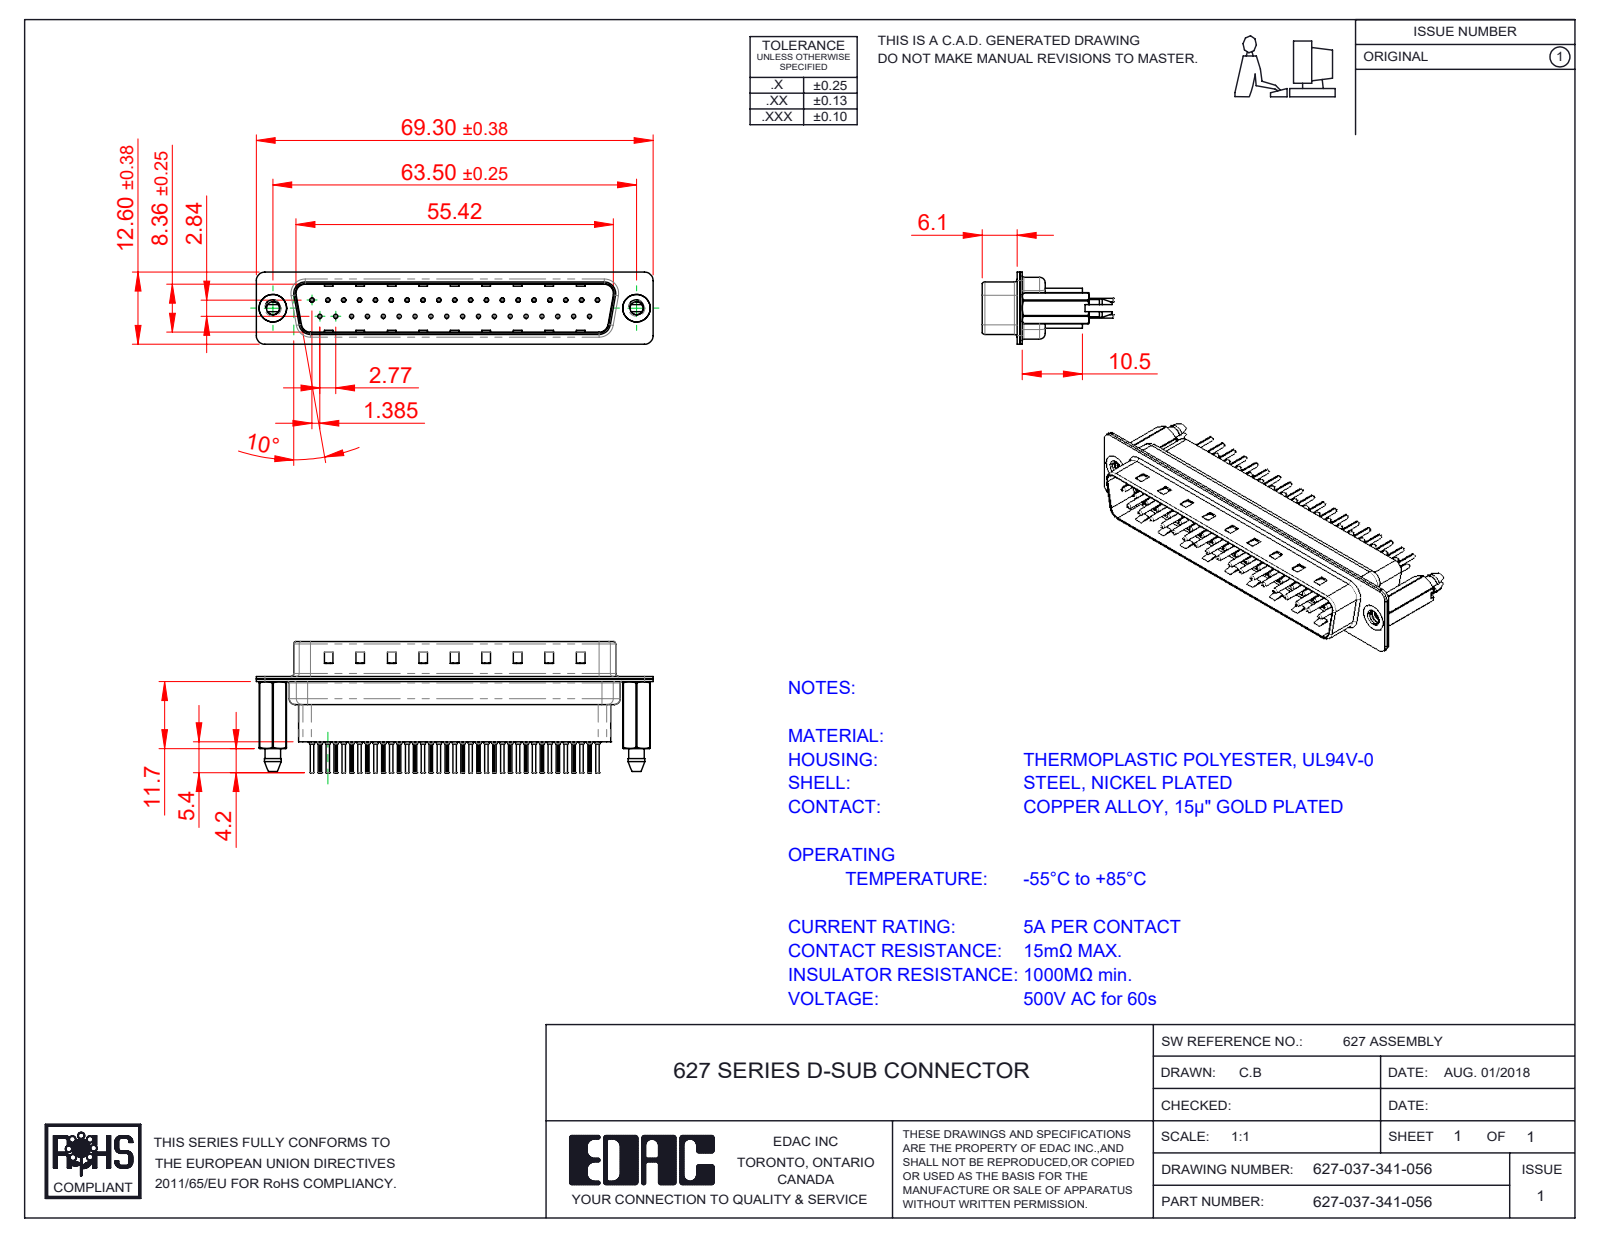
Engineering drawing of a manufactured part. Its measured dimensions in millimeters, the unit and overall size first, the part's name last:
Units: millimetres
Overall size (bounding box): 69.3 × 22.8 × 12.6
Round holes (diameter × count): ⌀0.2 ×37, ⌀0.35 ×37, ⌀1.1 ×37, ⌀1.6 ×37, ⌀2.26 ×2, ⌀4 ×2, ⌀4.8 ×2
Round bosses / shafts (diameter × count): ⌀2 ×37, ⌀1.5 ×37, ⌀0.75 ×37, ⌀0.6 ×37, ⌀4.9 ×2
Partial cylindrical surfaces — rounded edges, fillets, slot ends (radius × count): R0.1 ×74, R1.5 ×18, R2 ×12, R1.6 ×10, R0.5 ×8, R0.25 ×4, R0.6 ×4, R0.65 ×4
Main face-to-face distances: 0.4, 0.82, 9.58, 0.68, 7.68, 0.45, 1.5, 1.08, 8.08, 8.76
Hole centre spacings: 3.16, 2.77, 5.54, 8.31, 5.04, 10.1, 11.08, 12.78
Volume: 5 605 mm³ · Surface area: 14 398 mm²
Bodies: 42 solids, 4146 faces (1123 planar, 1576 cylindrical, 1447 other)
Part name (STEP PRODUCT): 627 4-40 Threaded Boardlock_HP41; 627 Contact Row 1_41; 627-037-341-056; 627 Shell Front_37 Contacts (+3 more)
STEP written by: SolidWorks 2020 (CONFIG_CONTROL_DESIGN)
